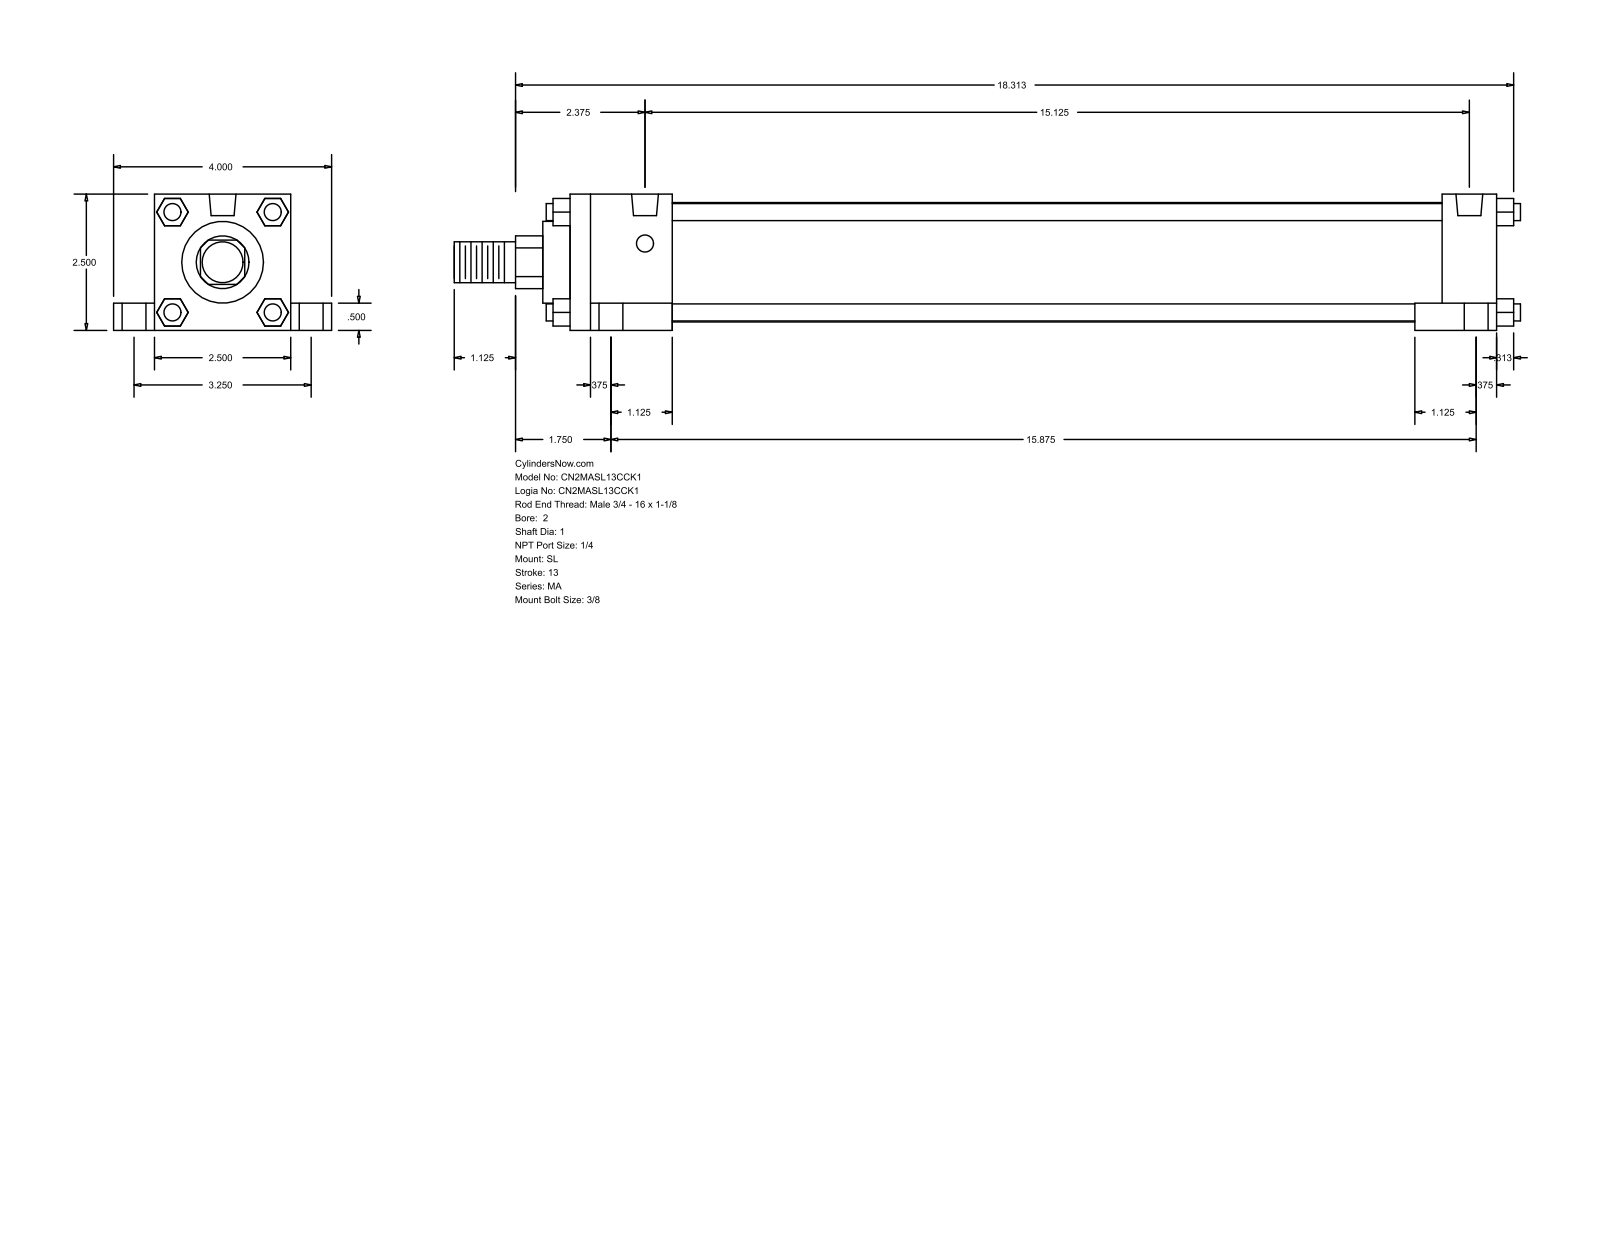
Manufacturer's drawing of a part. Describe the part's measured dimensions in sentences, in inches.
The part is named "MA_SL__0200_1". Its 3-D file was written by "GSSL Pune (CONFIG_CONTROL_DESIGN)". It is 0 solids with 148 faces: 112 planar, 36 cylindrical and 0 other. Overall it measures 19.563 by 4 by 2.5 inches. Round holes: 4 of diameter 0.313, 4 of diameter 0.437, 4 of diameter 0.687, 2 of diameter 0.492. Round bosses or shafts: 4 of diameter 0.313, 1 of diameter 2.19, 1 of diameter 1.5, 1 of diameter 1, 1 of diameter 0.75. Partial cylindrical surfaces (rounded edges, fillets, slot ends): 1 of radius 0.484. The main face-to-face distances are 2.5, 0.5, 17, 0.75, 3.25, 1, 2, 1.875, 15.125, 16. The hole center spacings are 1.63, 1.741, 3.25, 15.125, 15.336, 15.833, 15.875, 16.204.
